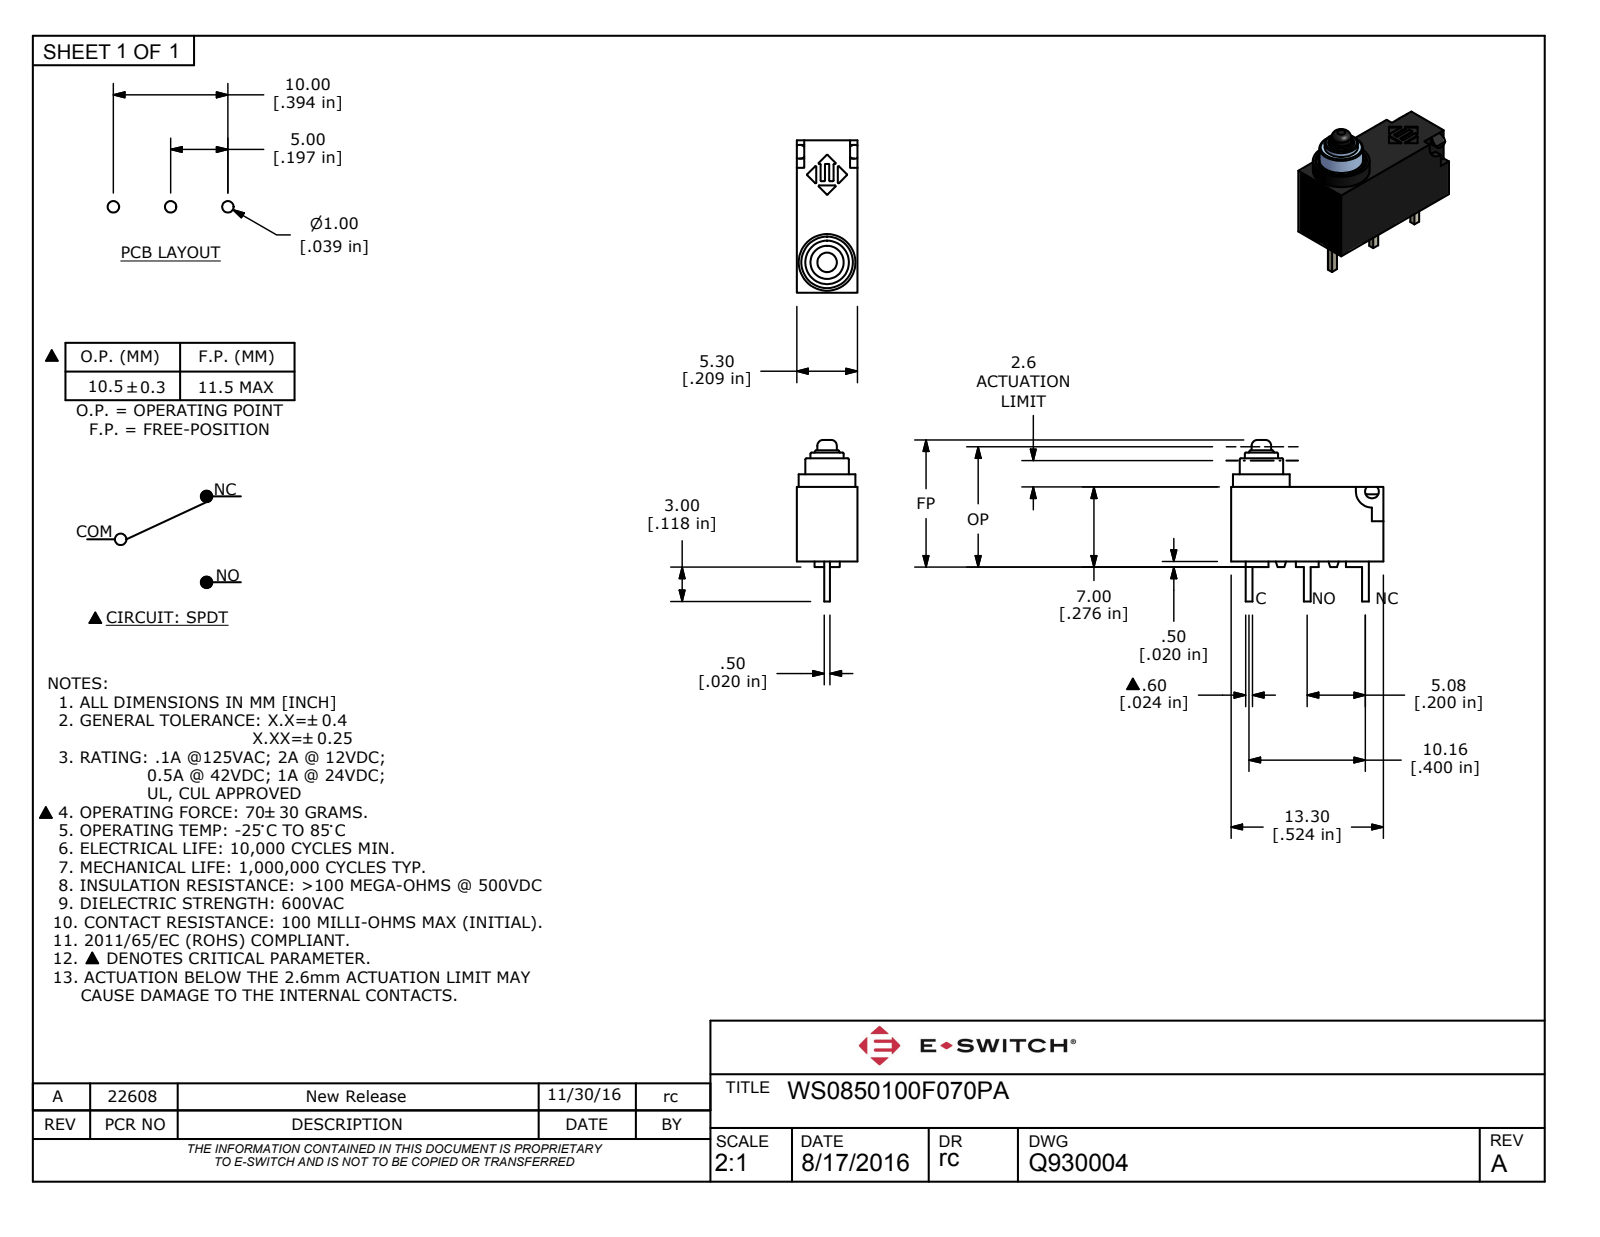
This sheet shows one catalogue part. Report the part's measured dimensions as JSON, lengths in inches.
{"part_name": "P:\\\\E-Switch Secure\\\\3D_MODELS_STP_FORMAT\\\\WS0850100F070PA.stp", "step_written_by": "ACIS (CONFIG_CONTROL_DESIGN)", "units": "inches", "bodies": {"solids": 1, "faces": 127, "planar": 91, "cylindrical": 29, "other": 7}, "overall_size": [0.555, 0.524, 0.209], "volume_in3": 0.03, "surface_area_in2": 0.732, "round_holes": [[0.177, 1]], "round_bosses_or_shafts": [[0.195, 1], [0.15, 1], [0.114, 1], [0.067, 1]], "partial_cylinders_radius": [[0.024, 1], [0.055, 1]], "face_to_face_distances": [0.209, 0.256, 0.524, 0.114, 0.094, 0.02, 0.252, 0.024, 0.183, 0.026]}
